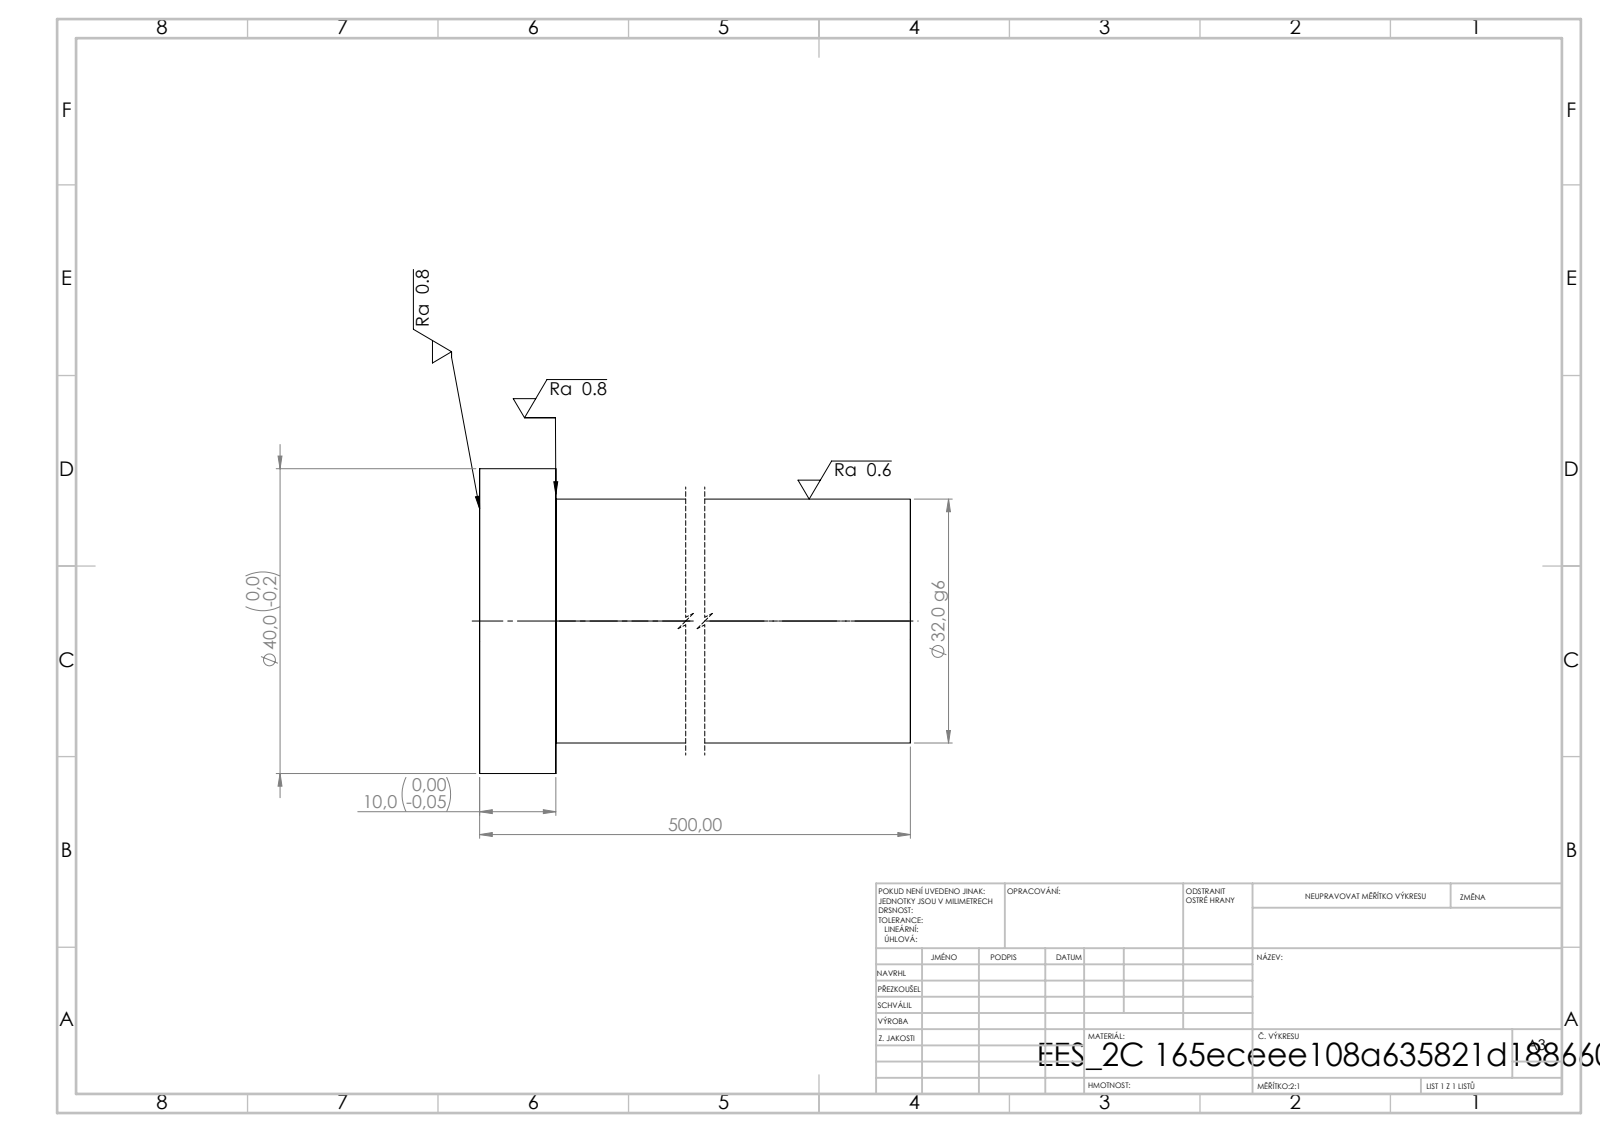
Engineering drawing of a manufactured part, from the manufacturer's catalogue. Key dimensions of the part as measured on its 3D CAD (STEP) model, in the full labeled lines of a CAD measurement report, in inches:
STEP written by: SolidWorks 2019 (CONFIG_CONTROL_DESIGN)
Units: inches
Bodies: 1 solid, 7 faces (3 planar, 4 cylindrical, 0 other)
Overall size (bounding box): 19.685 × 1.575 × 1.575
Volume: 24.82 in³ · Surface area: 82.2 in²
Round bosses / shafts (diameter × count): ⌀1.575 ×1, ⌀1.26 ×1
Main face-to-face distances: 19.685, 0.394, 19.291
